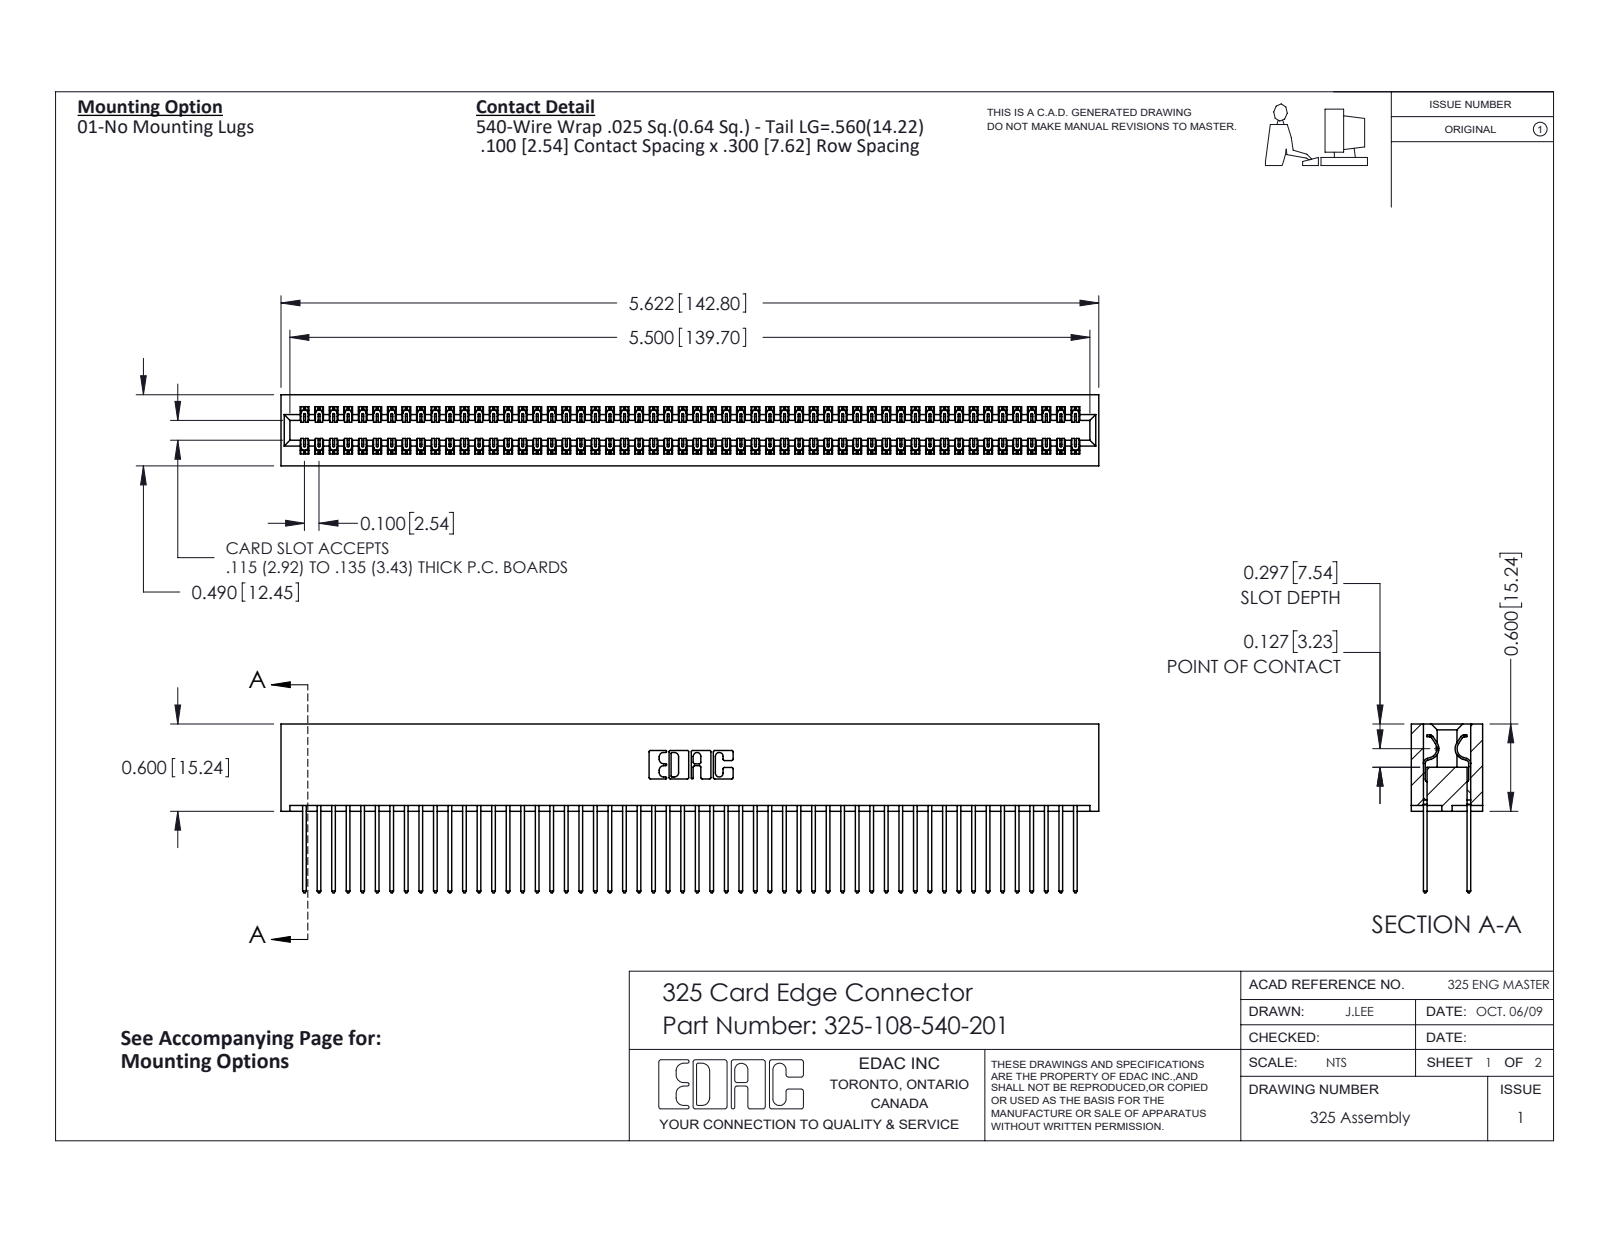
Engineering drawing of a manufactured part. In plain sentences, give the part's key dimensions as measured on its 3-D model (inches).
The part is named "325-292-001_325-293-140; 325-108-540-201; 325 Part_Lugless". Its 3-D file was written by "SolidWorks 2016 (CONFIG_CONTROL_DESIGN)". It is 109 solids with 5722 faces: 3954 planar, 1768 cylindrical and 0 other. Overall it measures 5.622 by 1.16 by 0.49 inches. Its volume is 1.194 cubic inches and its surface area 41.18 square inches. Partial cylindrical surfaces (rounded edges, fillets, slot ends): 162 of radius 0.006, 108 of radius 0.01, 22 of radius 0.01, 6 of radius 0.007, 6 of radius 0.031, 3 of radius 0.026, 2 of radius 0.014, 2 of radius 0.022. The main face-to-face distances are 0.083, 0.407, 0.3, 0.107, 0.383, 0.025, 0.325, 0.49, 0.275, 0.56.
